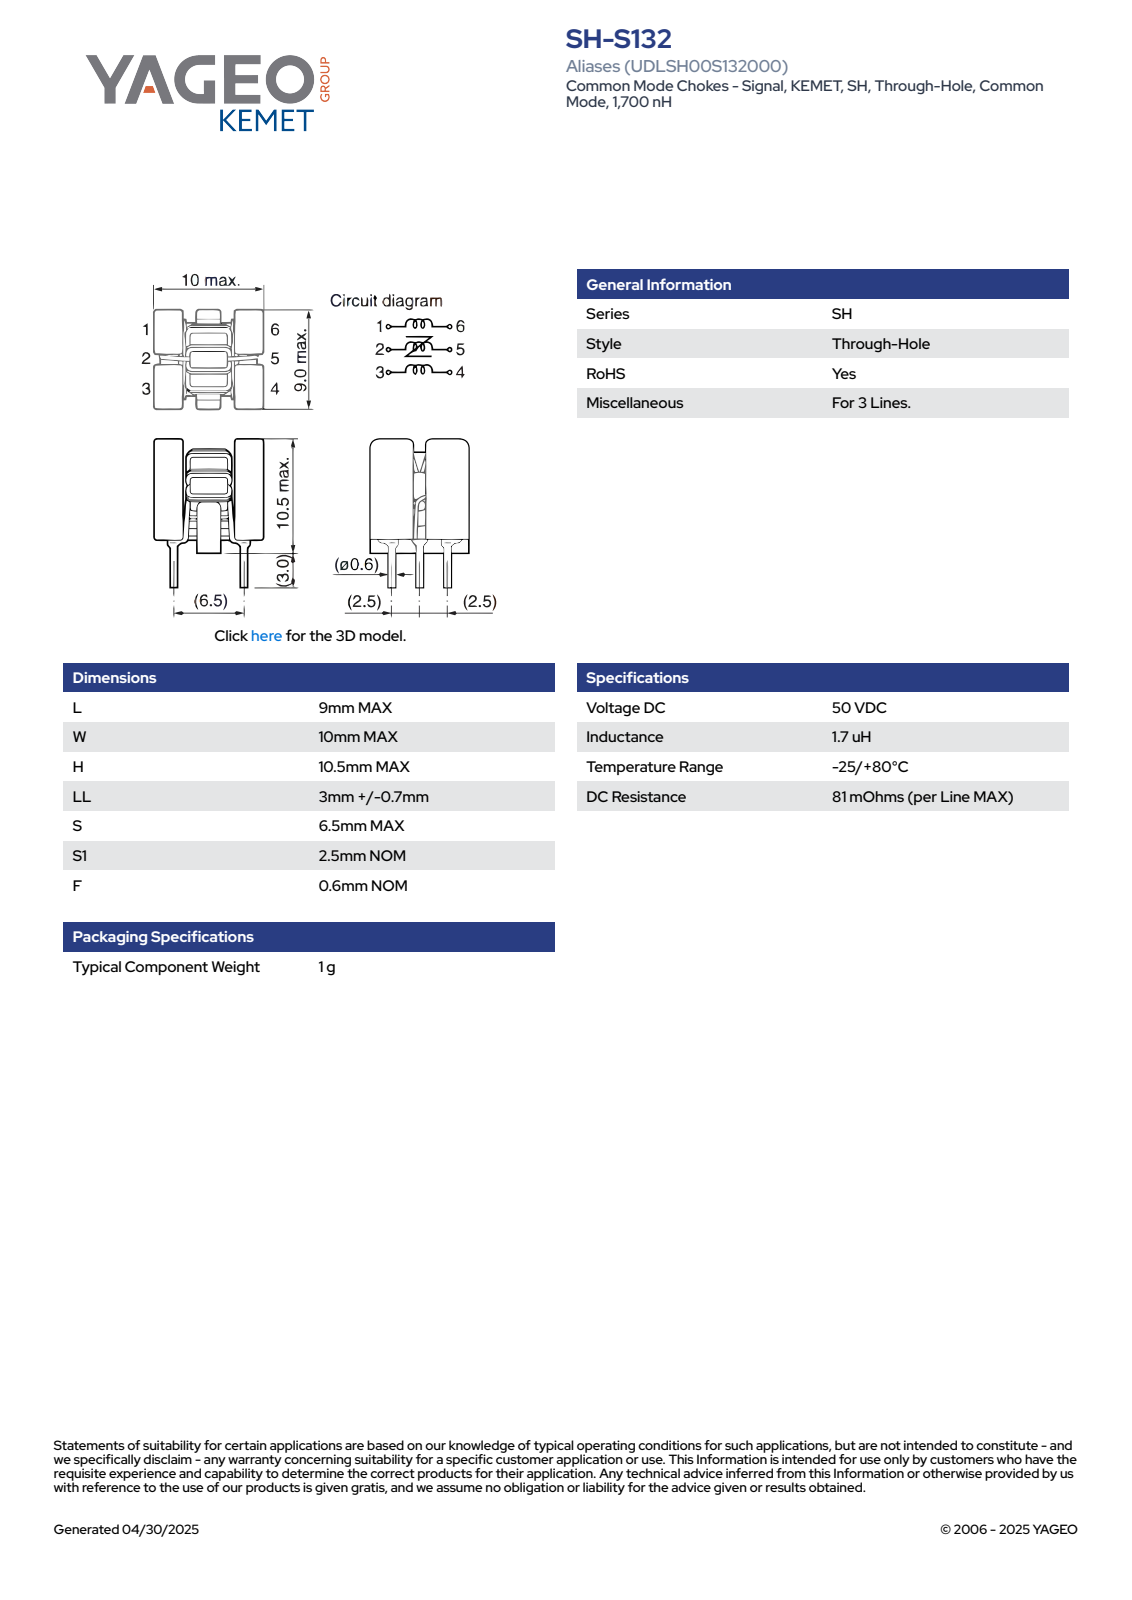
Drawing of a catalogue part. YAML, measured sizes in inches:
part_name: "IFC_DCSH5_L9W10H10.5"
step_written_by: "SolidWorks 2014 (AUTOMOTIVE_DESIGN)"
units: inches
bodies: {solids: 13, faces: 498, planar: 124, cylindrical: 254, other: 120}
overall_size: [0.532, 0.394, 0.354]
volume: 0.035
surface_area: 1.48
round_holes:
  - {diameter: 0.084, count: 1}
round_bosses_or_shafts:
  - {diameter: 0.01, count: 36}
  - {diameter: 0.024, count: 6}
  - {diameter: 0.226, count: 1}
partial_cylinders:
  - {radius: 0.01, count: 38}
  - {radius: 0.005, count: 5}
face_to_face_distances: [0.083, 0.311, 0.118, 0.157, 0.198, 0.394, 0.228, 0.354, 0.193, 0.276]
